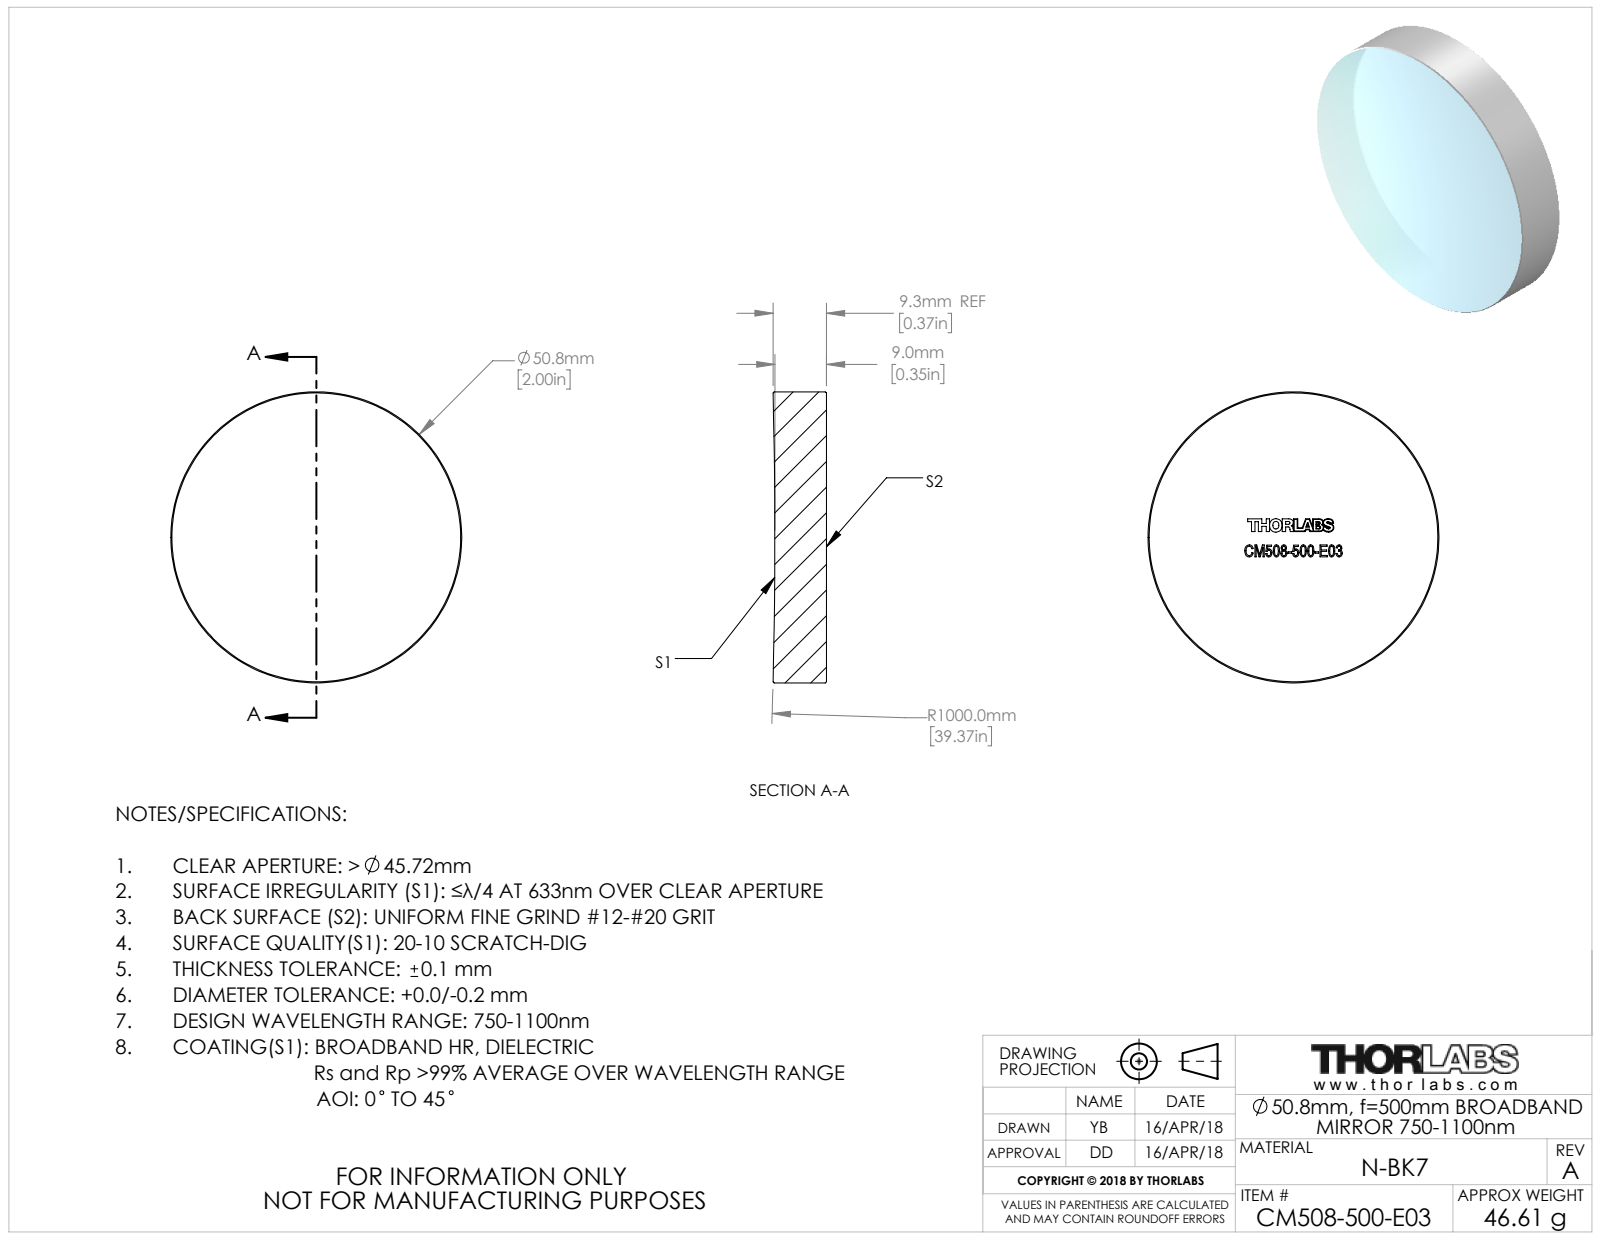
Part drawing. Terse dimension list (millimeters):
name: TTN153328-E0W
written by: SolidWorks 2018 (CONFIG_CONTROL_DESIGN)
unit: mm
bodies: 1 solid, 43 faces (35 planar, 2 cylindrical, 6 other)
size: 50.8 × 50.8 × 9.32
volume: 18 562 mm³; area: 5 504 mm²
bosses: 1× ⌀50.8
